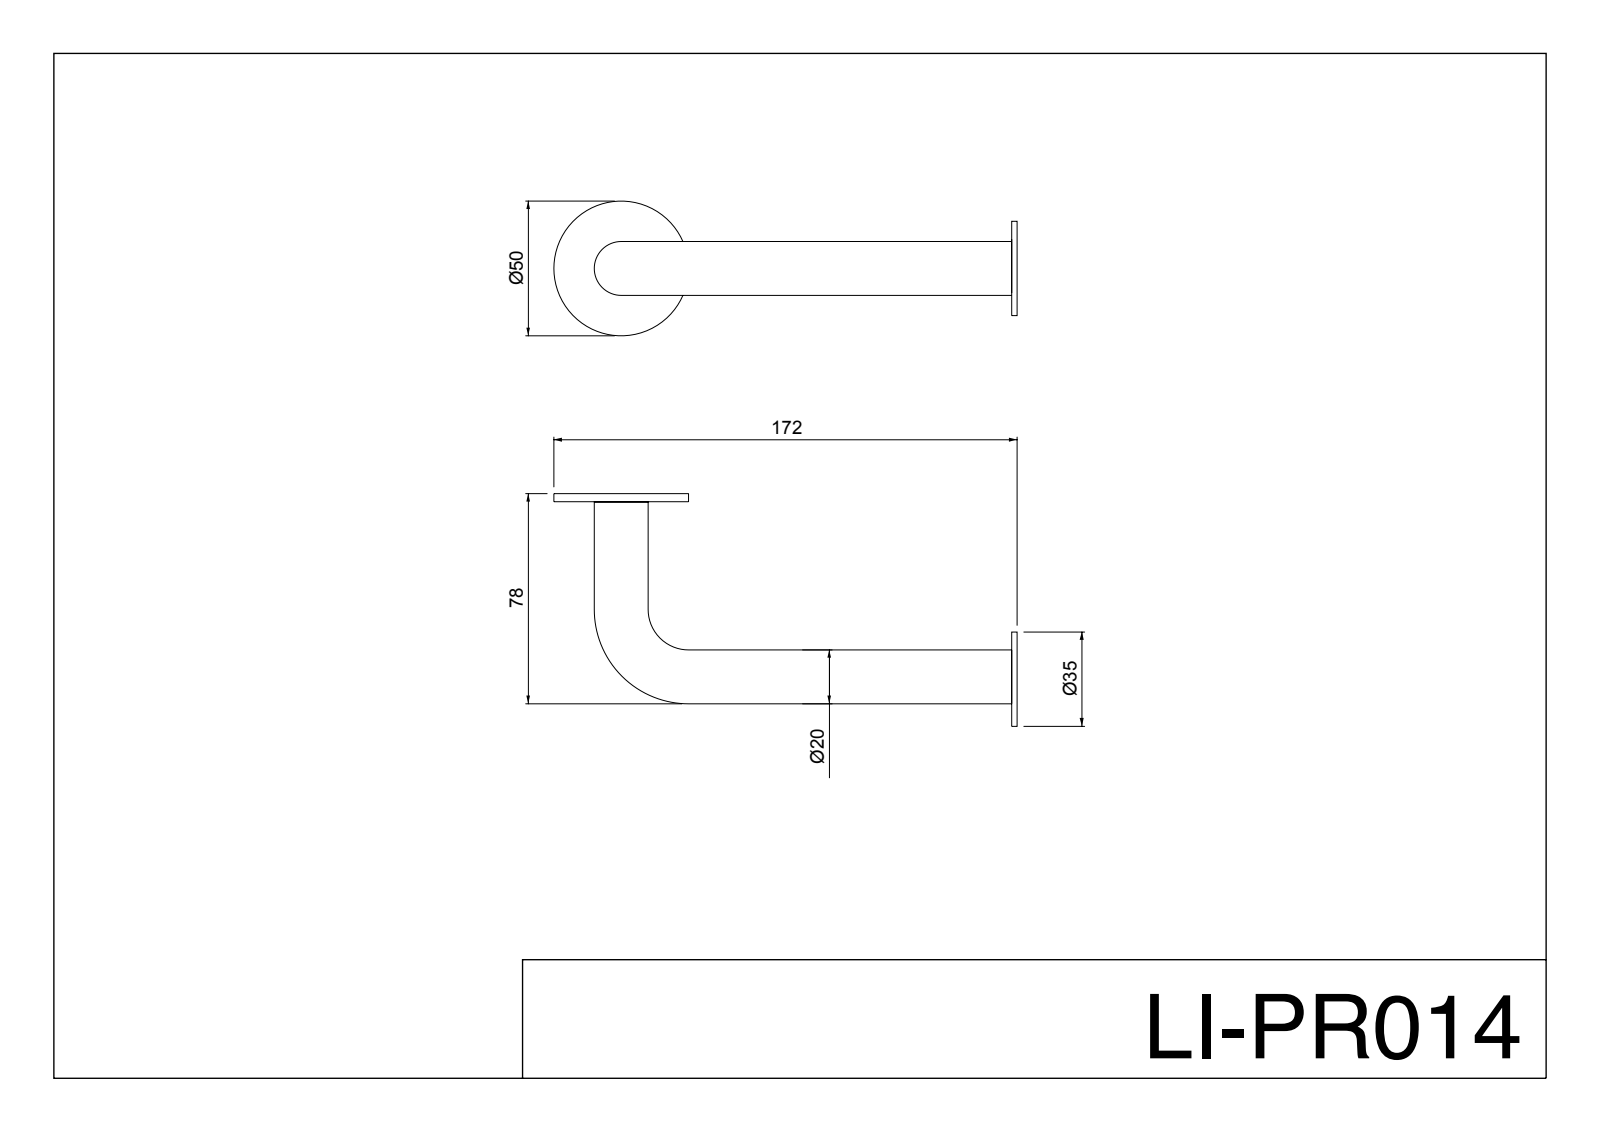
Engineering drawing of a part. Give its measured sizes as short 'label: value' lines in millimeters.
written by: ST-DEVELOPER v15 (AUTOMOTIVE_DESIGN)
unit: mm
bodies: 3 solids, 26 faces (6 planar, 0 cylindrical, 20 other)
size: 167 × 89.63 × 40
volume: 74 466 mm³; area: 18 563 mm²
face distances: 8, 2
